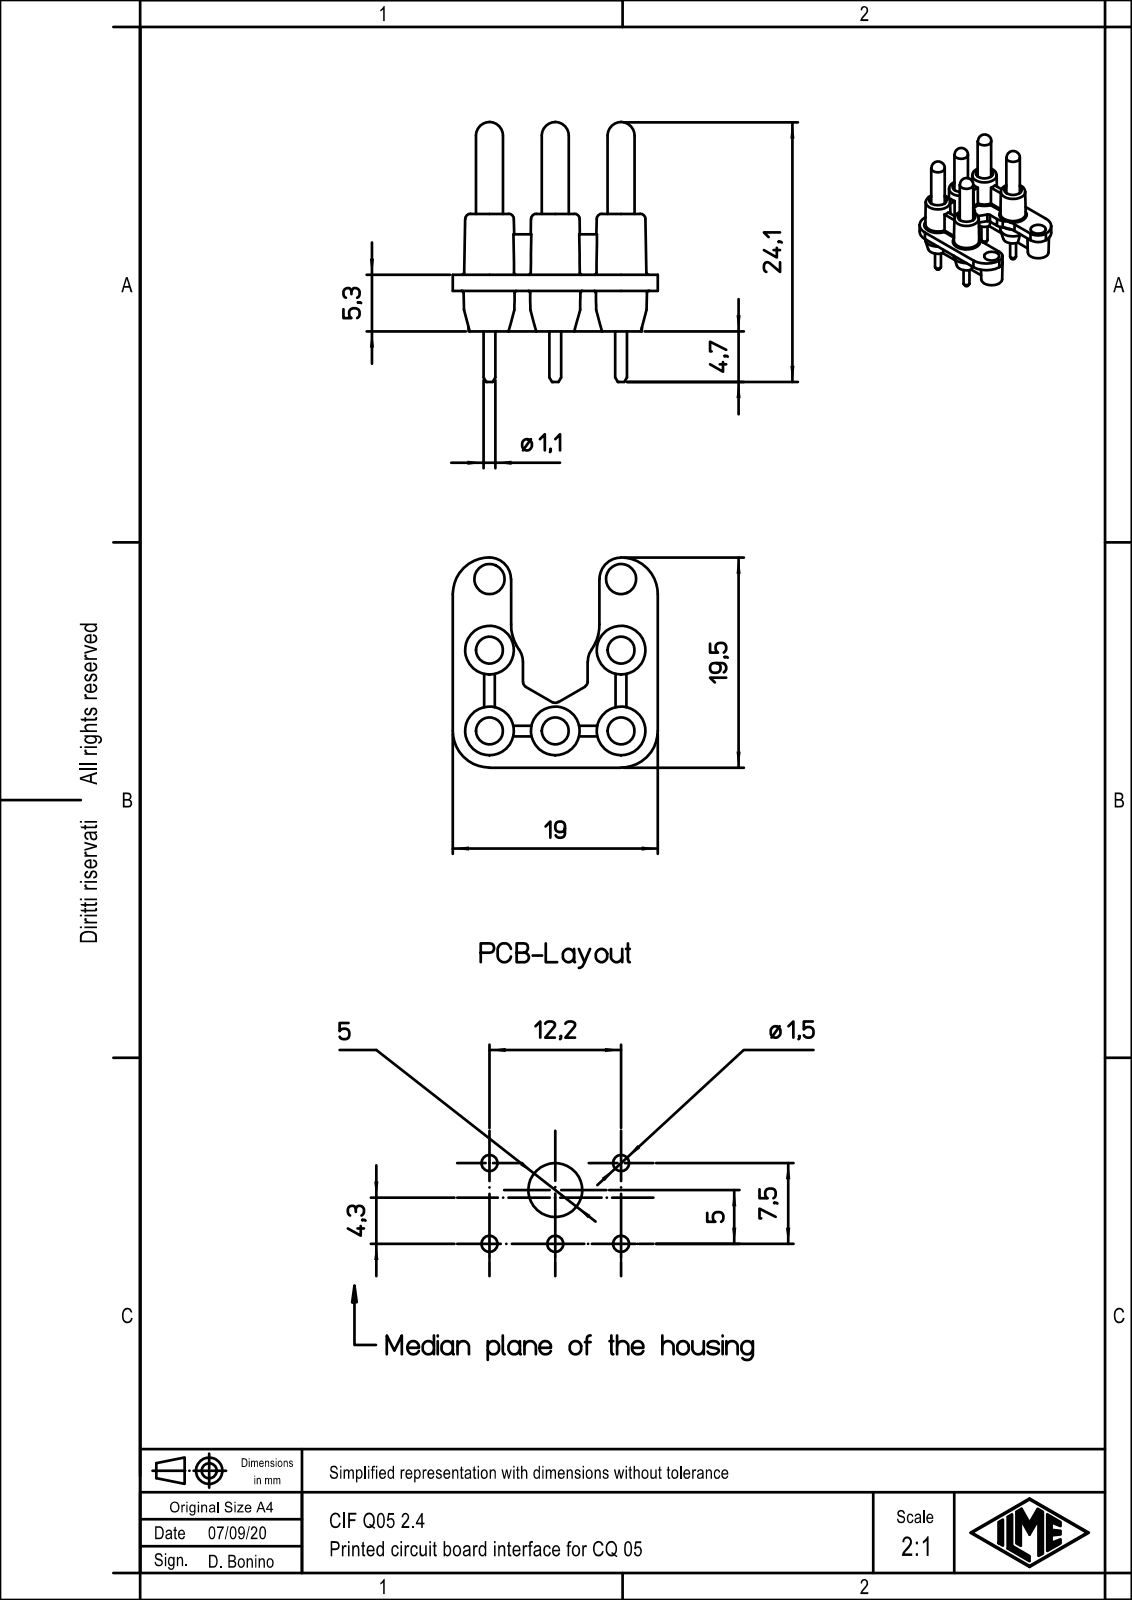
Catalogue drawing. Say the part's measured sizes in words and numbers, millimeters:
The part is named "CIF_Q05_2.4". Its 3-D file was written by "Creo Elements/Direct Modeling 20.1B 02-Apr-2019 (C) Parametric Technology GmbH (AUTOMOTIVE_DESIGN)". It is 1 solid with 144 faces: 47 planar, 57 cylindrical and 40 other. Overall it measures 24.1 by 19.5 by 19 millimeters. Its volume is 1 503 cubic millimeters and its surface area 1 940 square millimeters. Round holes: 2 of diameter 2.4. Round bosses or shafts: 5 of diameter 4.8, 5 of diameter 4.5, 5 of diameter 2.5, 5 of diameter 1.1, 2 of diameter 4. Partial cylindrical surfaces (rounded edges, fillets, slot ends): 4 of radius 3.4, 3 of radius 0.5, 2 of radius 2, 1 of radius 4.1. The main face-to-face distances are 1.5, 3.75, 5.25, 1, 12.2, 2.9, 3.9, 15.1, 16.1, 13.2. The hole center spacings are 12.2.
